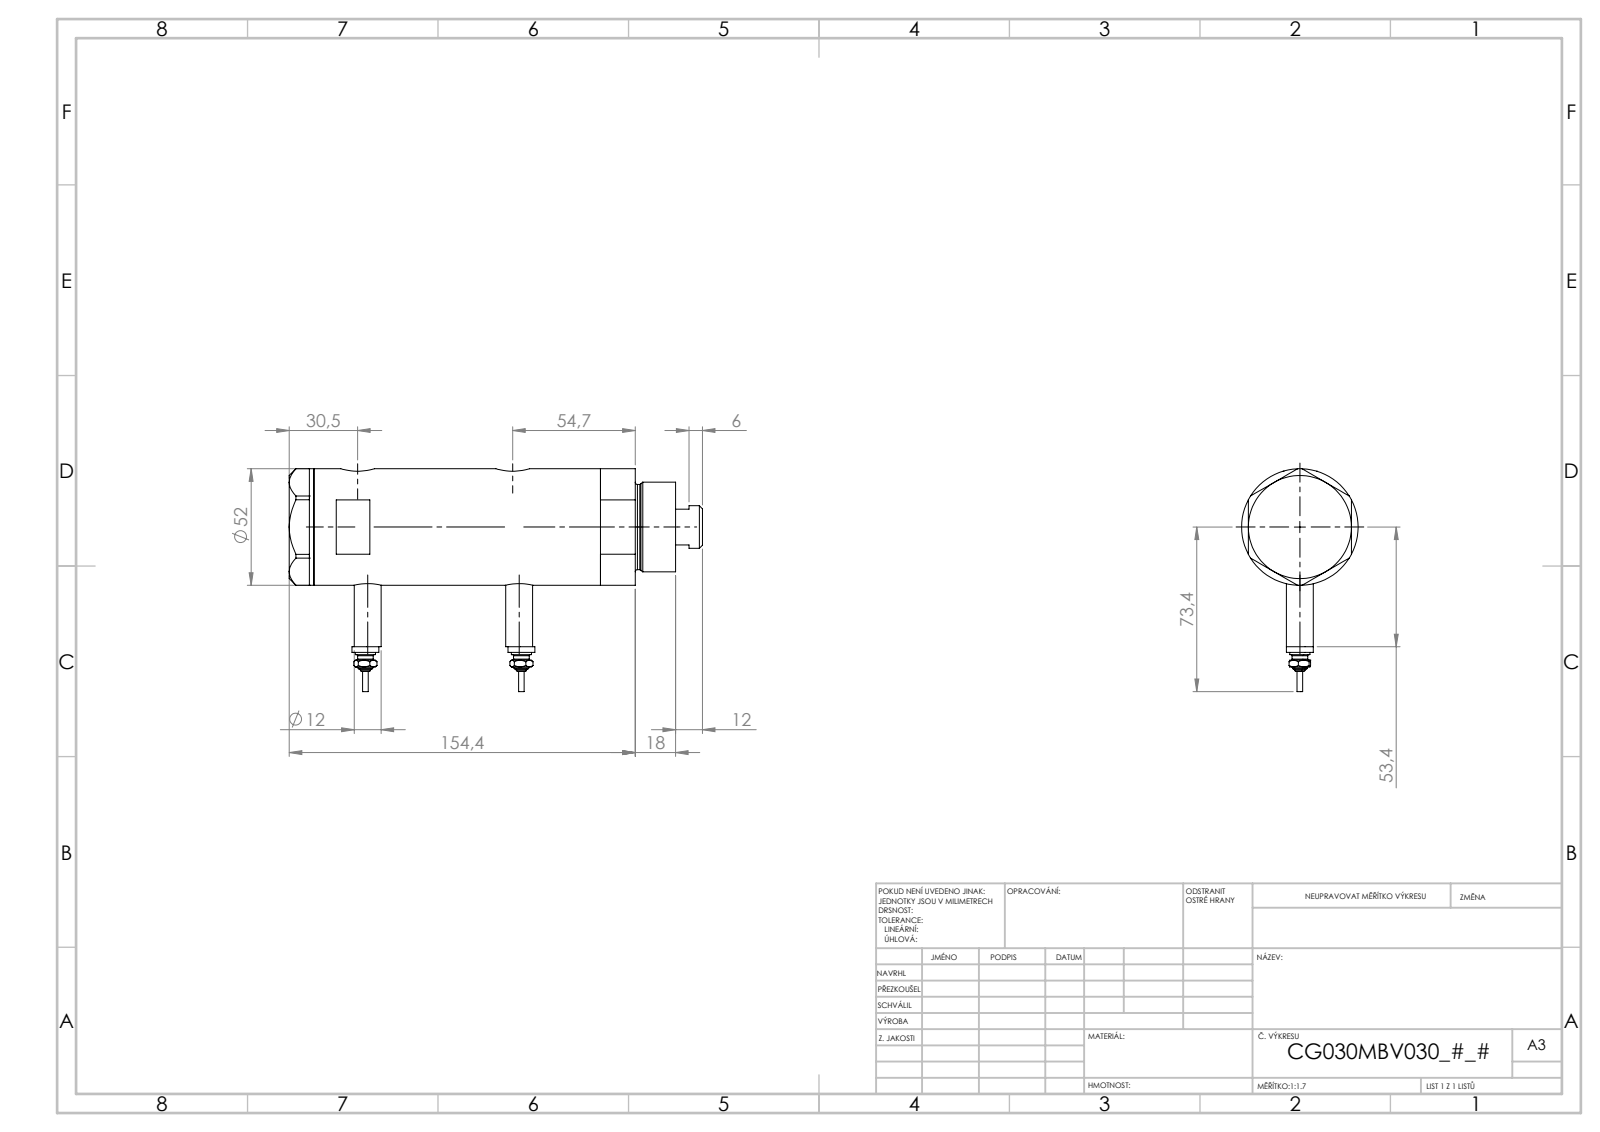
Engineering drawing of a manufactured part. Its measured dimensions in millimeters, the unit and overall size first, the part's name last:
Units: millimetres
Overall size (bounding box): 179.02 × 84.3 × 52
Round holes (diameter × count): ⌀5 ×2, ⌀9.73 ×2, ⌀12.5 ×2, ⌀15 ×2, ⌀6.5 ×1, ⌀20 ×1, ⌀21.5 ×1, ⌀30 ×1, ⌀33 ×1, ⌀44 ×1
Round bosses / shafts (diameter × count): ⌀12 ×3, ⌀9 ×2, ⌀7 ×2, ⌀4.34 ×2, ⌀2.4 ×2, ⌀52 ×1, ⌀40 ×1, ⌀38 ×1
Main face-to-face distances: 23.81, 10.99, 34.8, 46, 94.55, 83.56, 59.75, 130.95, 119.96, 96.15
Hole centre spacings: 2.9, 4.5, 56.75, 59.65, 61.25, 64.15, 2.89, 2.91
Volume: 322 306 mm³ · Surface area: 76 649 mm²
Bodies: 6 solids, 246 faces (95 planar, 77 cylindrical, 74 other)
Part name (STEP PRODUCT): V270CG_VC; V270CG_MIDDLE; V270CG_BACK; V270CG_SWITCH (+1 more)
STEP written by: SolidWorks 2019 (CONFIG_CONTROL_DESIGN)
